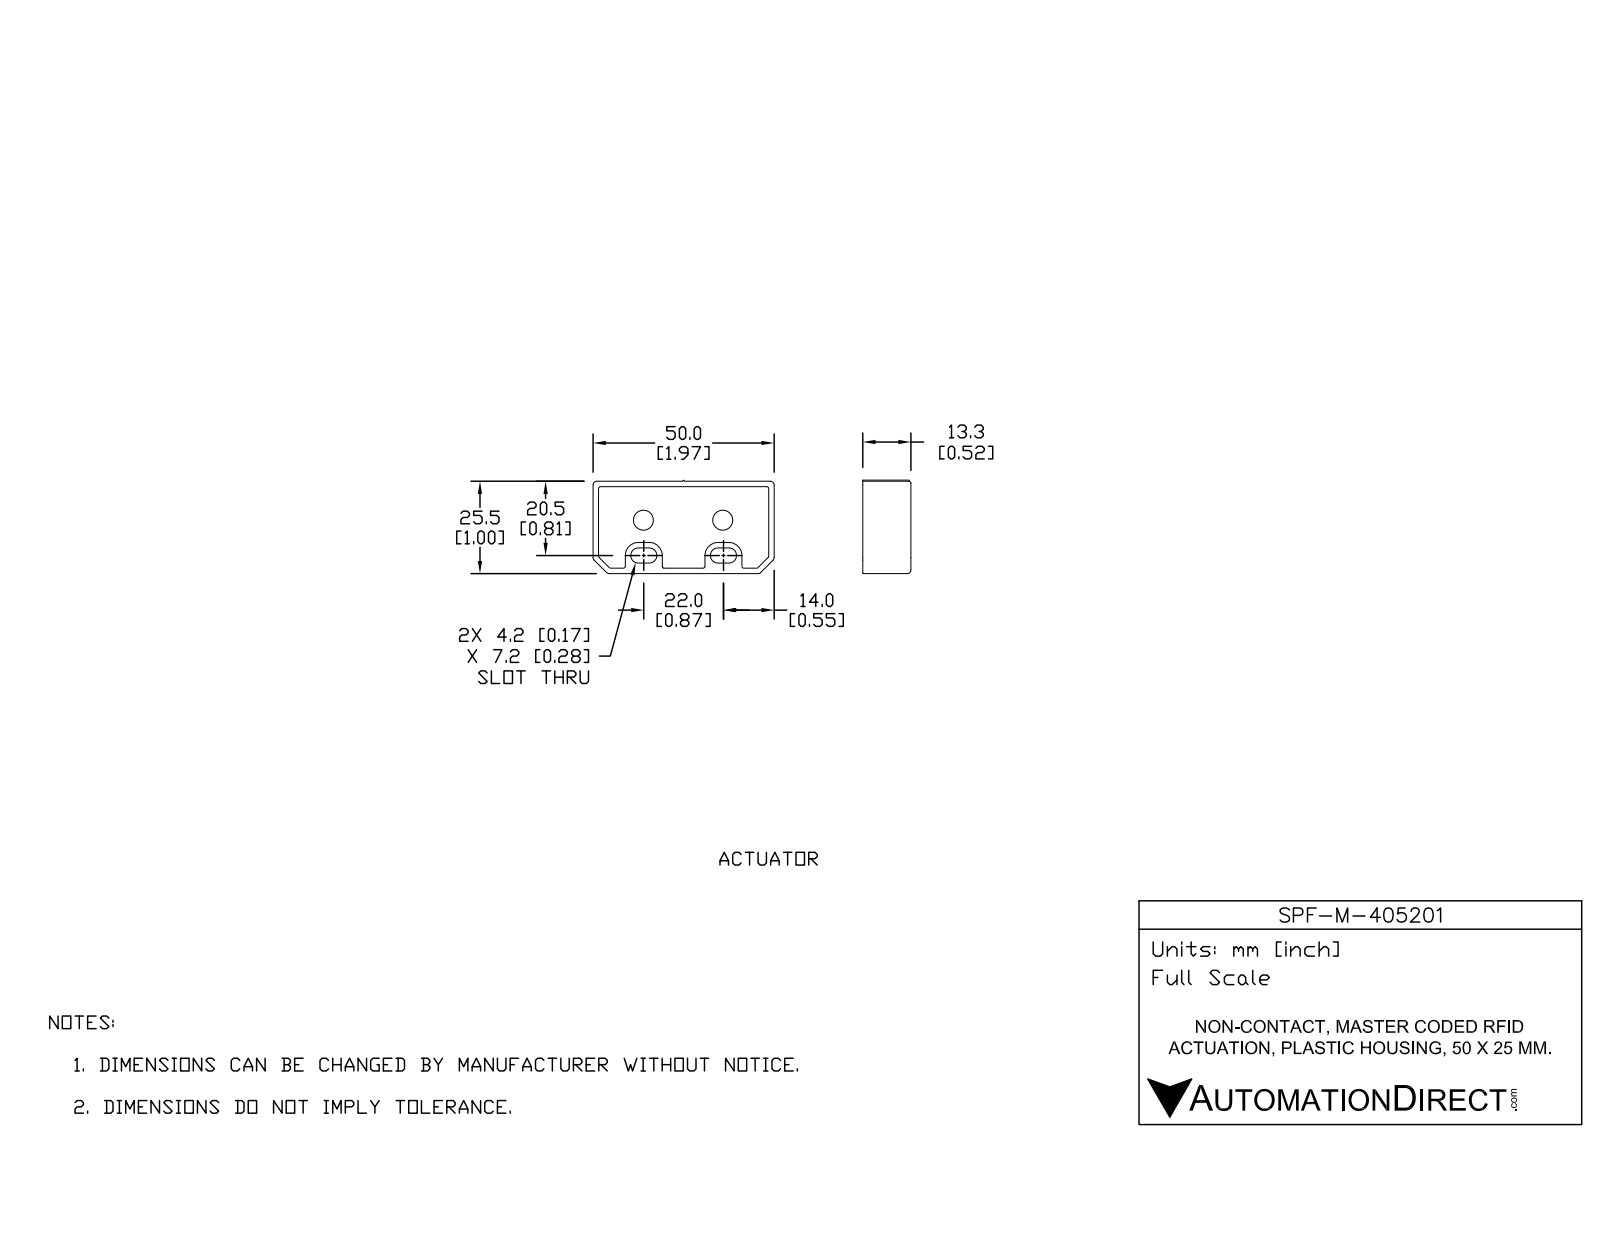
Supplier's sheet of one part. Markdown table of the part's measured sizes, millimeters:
| quantity | value |
| --- | --- |
| part name | SPF-M-405201 |
| STEP written by | SolidWorks 2017 (AUTOMOTIVE_DESIGN) |
| units | millimeters |
| bodies | 4 solids, 458 faces (211 planar, 138 cylindrical, 109 other) |
| overall size | 50 × 25.8 × 13.3 |
| volume | 6 510 mm³ |
| surface area | 9 600 mm² |
| round holes (diameter × count) | 5 × 2 |
| round bosses / shafts (diameter × count) | 4.9 × 2, 2 × 2 |
| partial cylindrical surfaces (radius × count) | 0.5 × 61, 1 × 21, 2 × 4, 2.1 × 4, 3.6 × 4, 3.6 × 4, 4.3 × 4, 4.6 × 4 |
| main face-to-face distances | 1.5, 11.6, 10.1, 1.2, 11.3, 12.8, 24, 48.5, 25.5, 13.1 |
| hole center spacings | 21.9 |
